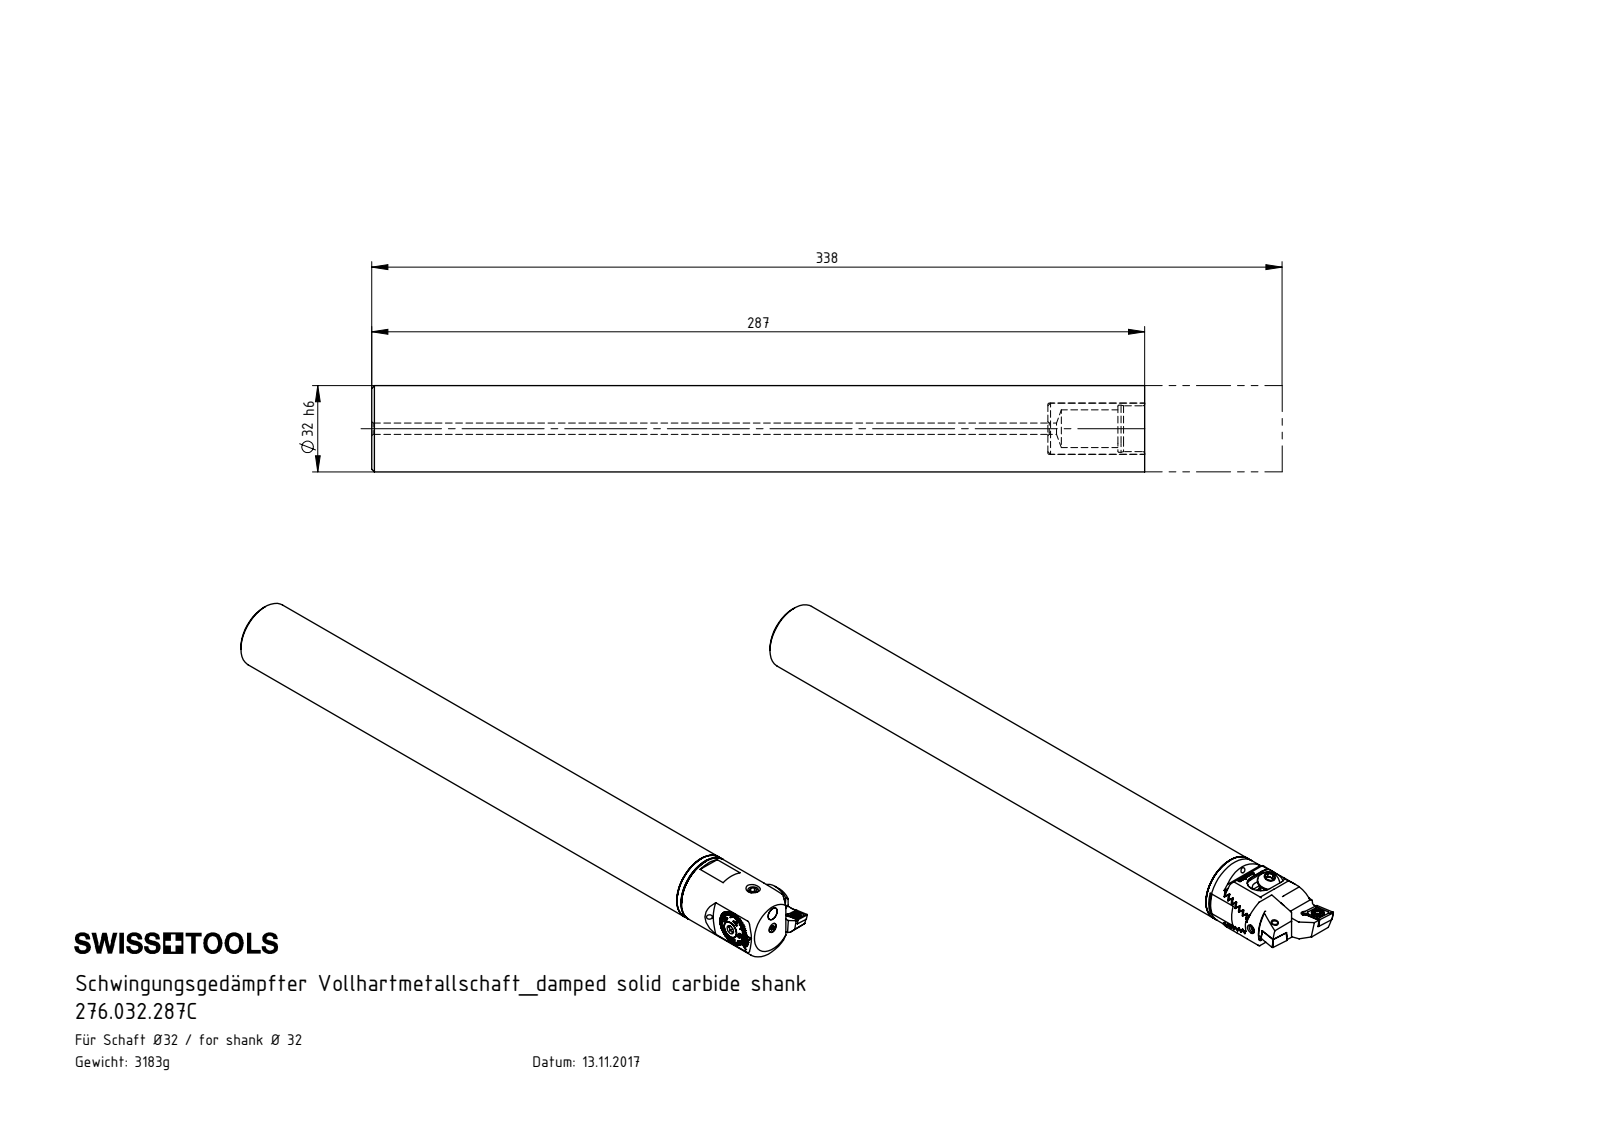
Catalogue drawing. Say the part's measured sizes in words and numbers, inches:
The part is named "Z32-ER3.001.013_A; CCMT09T304; WCB-ER2.001.009_A; Z32-xxx.001.021_B (+8 more)". Its 3-D file was written by "SolidWorks 2017 (CONFIG_CONTROL_DESIGN)". It is 18 solids with 1025 faces: 463 planar, 248 cylindrical and 314 other. Overall it measures 13.189 by 1.575 by 1.26 inches. Its volume is 15.49 cubic inches and its surface area 92.32 square inches. Round holes: 5 of diameter 0.098, 5 of diameter 0.13, 2 of diameter 0.063, 2 of diameter 0.079, 2 of diameter 0.173, 2 of diameter 0.197, 2 of diameter 0.24, 2 of diameter 0.252, 2 of diameter 0.268, 1 of diameter 0.138, 1 of diameter 0.165, 1 of diameter 0.402. Round bosses or shafts: 4 of diameter 0.157, 2 of diameter 0.413, 2 of diameter 0.402, 2 of diameter 0.236, 2 of diameter 0.207, 1 of diameter 1.26, 1 of diameter 0.63, 1 of diameter 0.472. Partial cylindrical surfaces (rounded edges, fillets, slot ends): 16 of radius 0.02, 14 of radius 0.008, 12 of radius 0.008, 12 of radius 0.013, 12 of radius 0.023, 4 of radius 0.079, 4 of radius 0.13, 4 of radius 0.236. The main face-to-face distances are 0.094, 0.187, 0.281, 11.299, 0.375, 0.118, 11.417, 1.417, 9.882, 1.535. The hole center spacings are 0.239, 0.244, 0.954, 0.958, 1.128, 0.354, 0.355, 0.685.
